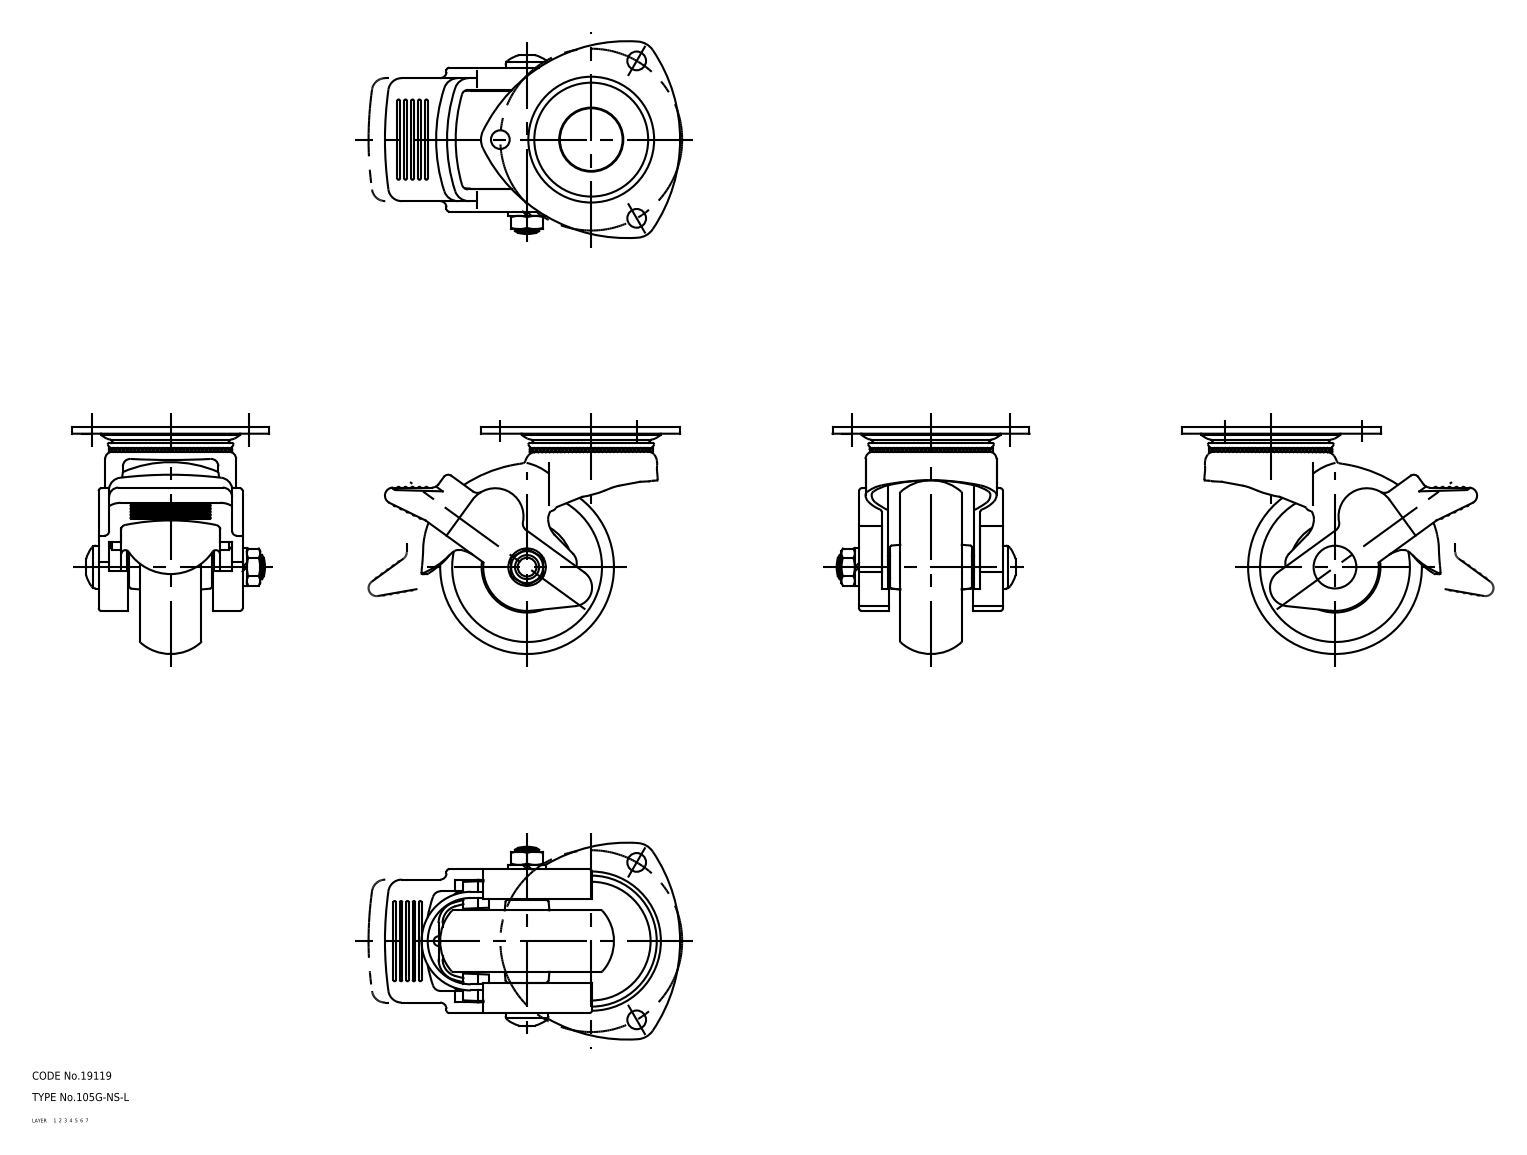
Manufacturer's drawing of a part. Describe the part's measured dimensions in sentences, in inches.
The part is named "lever; wheel; mounting plate; main shaft (+2 more)". Its 3-D file was written by "CADfix (AUTOMOTIVE_DESIGN)". It is 6 solids with 381 faces: 0 planar, 0 cylindrical and 381 other. Overall it measures 4.346 by 3.346 by 2.899 inches. Its volume is 8.382 cubic inches and its surface area 87.66 square inches.
